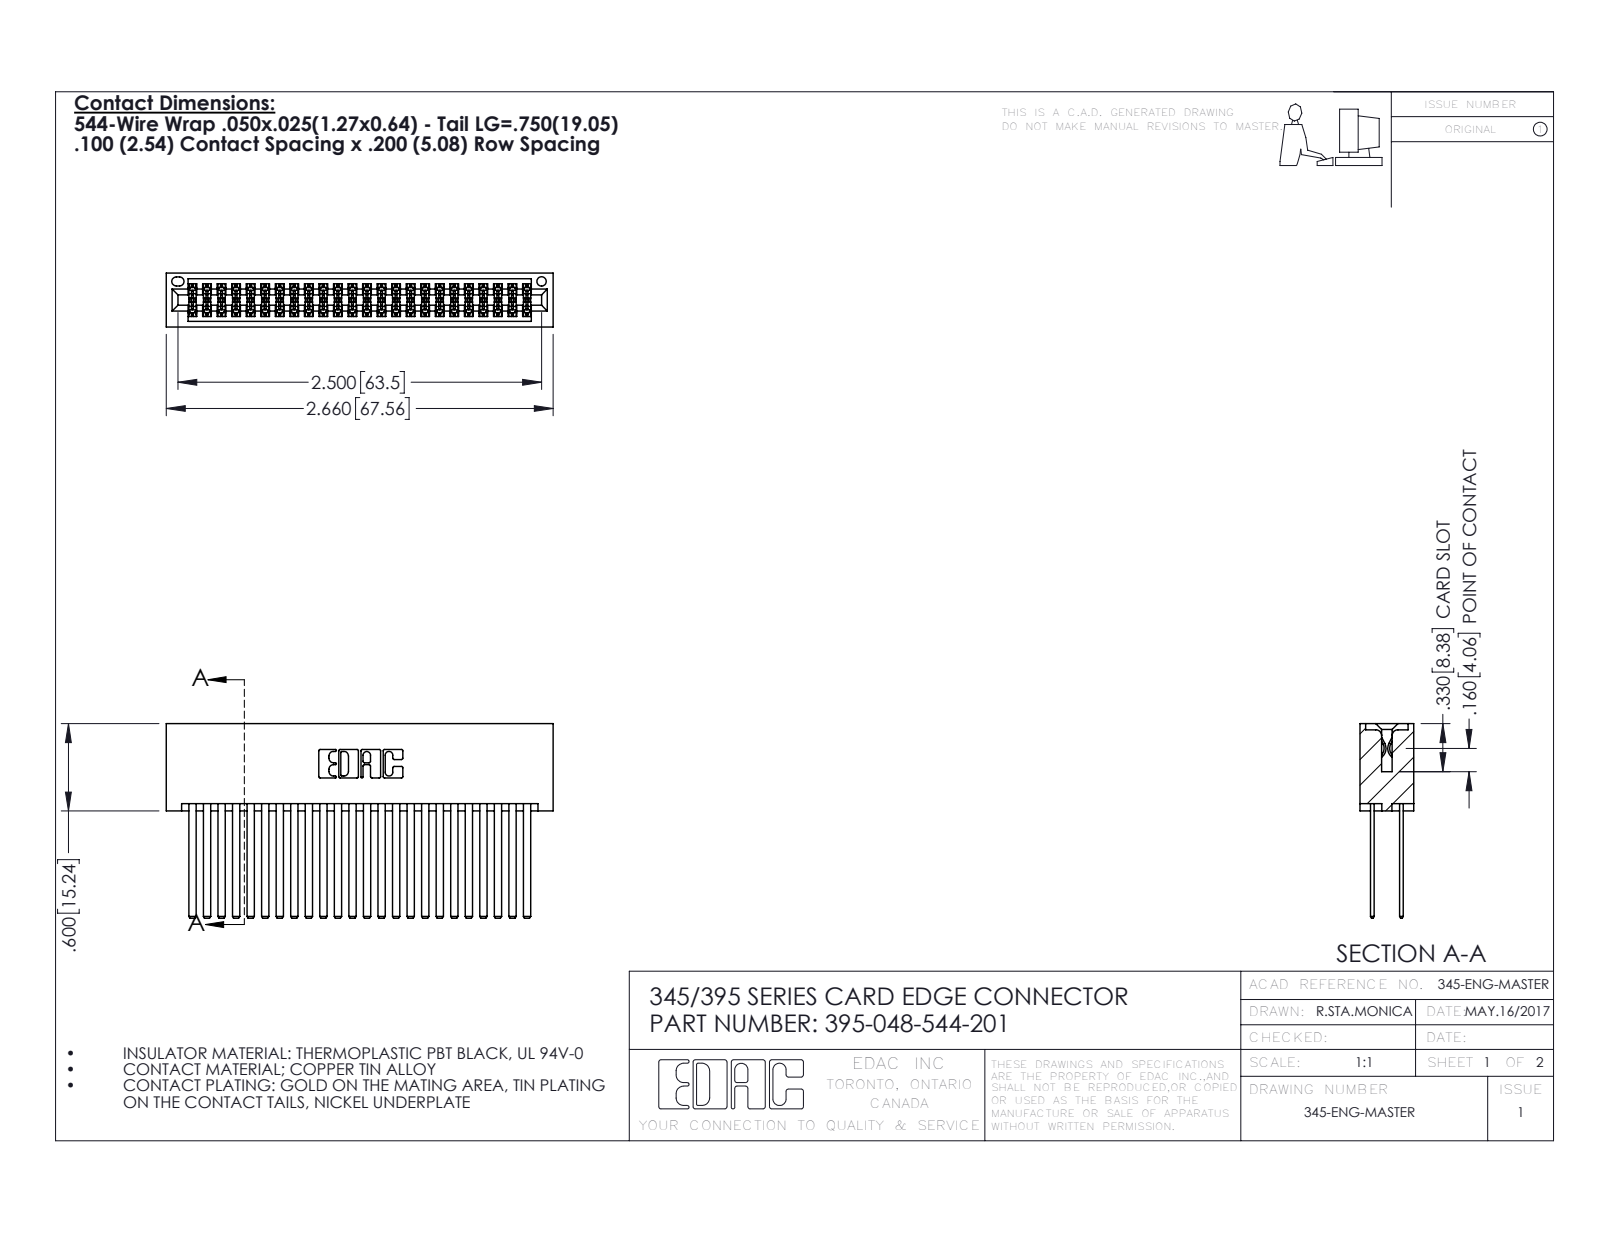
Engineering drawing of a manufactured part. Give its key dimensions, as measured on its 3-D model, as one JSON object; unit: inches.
{"part_name": "345-292-001_345-293-144; 395-048-544-201; 345 Part_No Mounting Lugs", "step_written_by": "SolidWorks 2016 (CONFIG_CONTROL_DESIGN)", "units": "inches", "bodies": {"solids": 49, "faces": 2230, "planar": 1468, "cylindrical": 762, "other": 0}, "overall_size": [2.66, 1.337, 0.37], "volume_in3": 0.469, "surface_area_in2": 20.59, "round_holes": [[0.064, 1]], "partial_cylinders_radius": [[0.006, 72], [0.01, 22], [0.007, 6], [0.031, 6], [0.026, 3], [0.014, 2], [0.019, 2], [0.022, 2]], "face_to_face_distances": [0.2, 0.025, 0.298, 0.072, 0.098, 0.272, 0.225, 0.175, 0.37, 0.05]}
